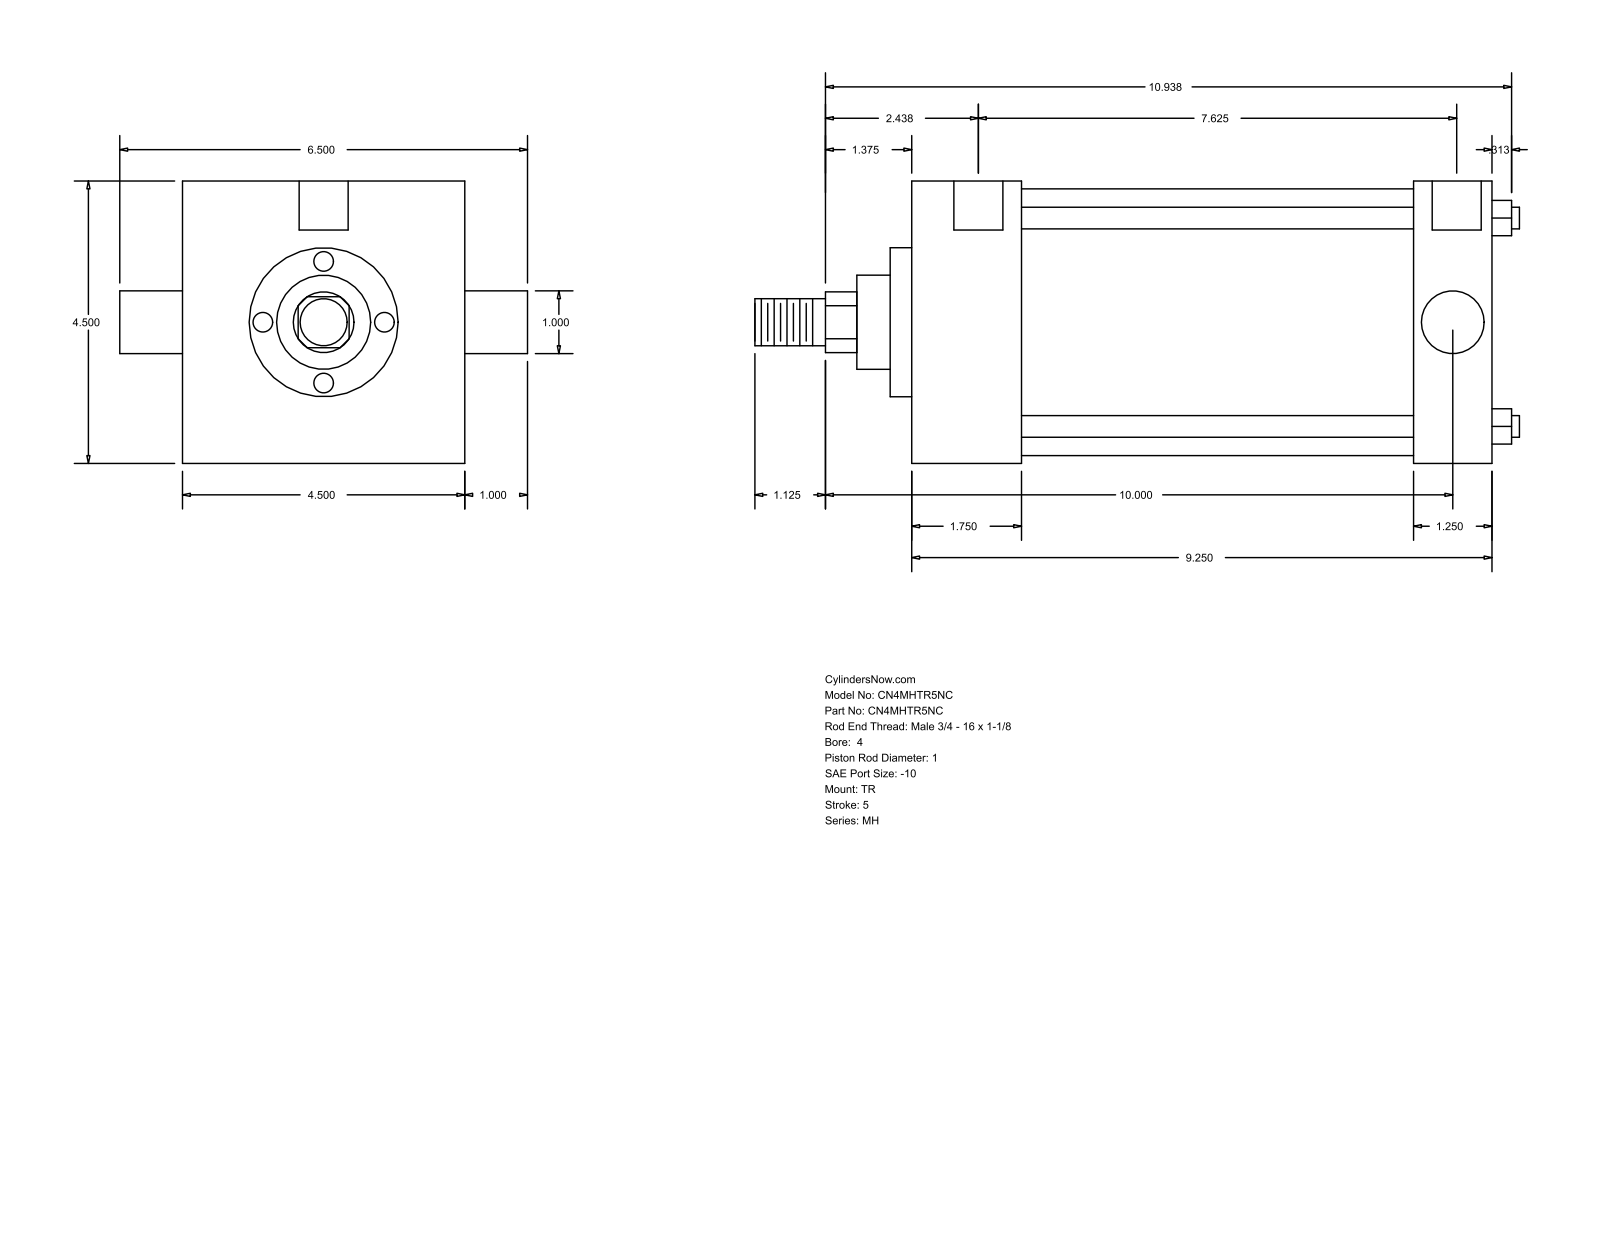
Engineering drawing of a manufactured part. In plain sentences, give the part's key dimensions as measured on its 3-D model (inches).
The part is named "MH_TR__0400_1". Its 3-D file was written by "GSSL Pune (CONFIG_CONTROL_DESIGN)". It is 0 solids with 86 faces: 61 planar, 25 cylindrical and 0 other. Overall it measures 12.187 by 6.5 by 4.5 inches. Round holes: 3 of diameter 0.344, 2 of diameter 0.781. Round bosses or shafts: 4 of diameter 0.345, 2 of diameter 1, 1 of diameter 4.25, 1 of diameter 2.375, 1 of diameter 1.5, 1 of diameter 0.75. Partial cylindrical surfaces (rounded edges, fillets, slot ends): 1 of radius 0.484. The main face-to-face distances are 4.5, 9.25, 1.75, 7.5, 8, 6.25, 1.25, 0.344, 2.094, 8.344. The hole center spacings are 0.062, 0.063, 7.625, 7.687, 7.688, 7.75.
